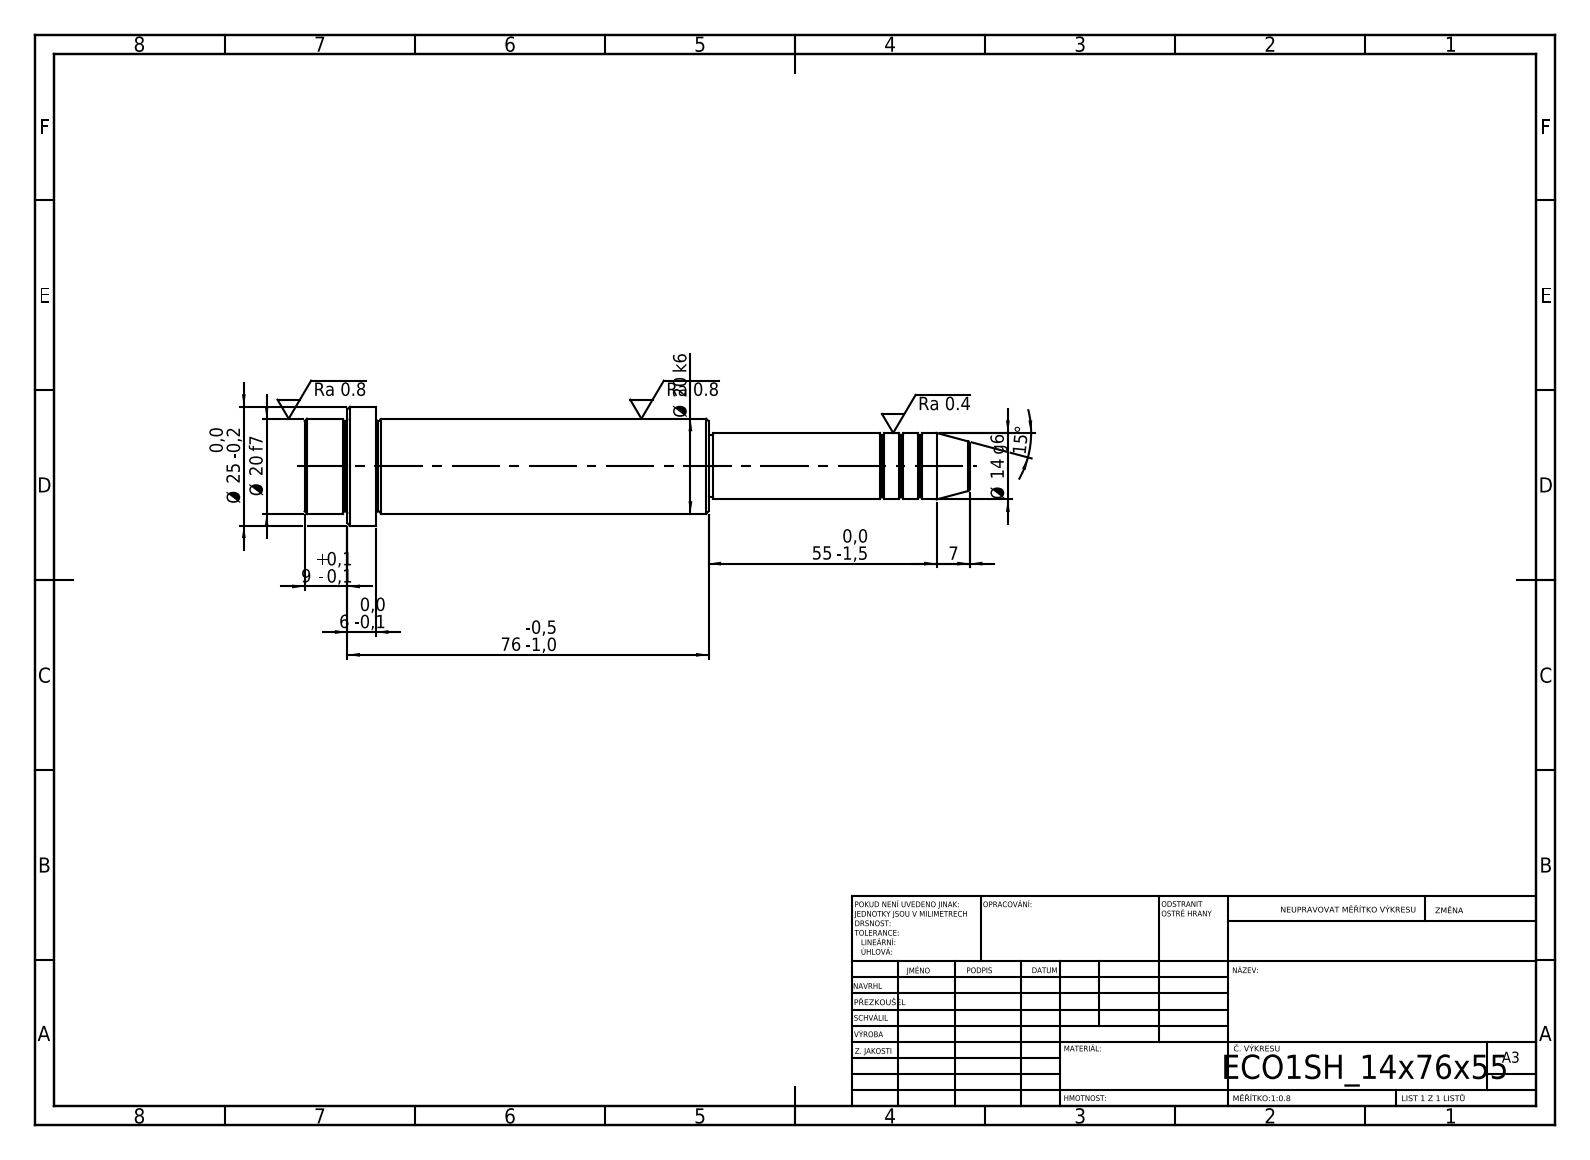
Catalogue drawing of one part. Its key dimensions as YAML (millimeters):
step_written_by: "SolidWorks 2019 (CONFIG_CONTROL_DESIGN)"
units: millimeters
bodies: {solids: 1, faces: 52, planar: 6, cylindrical: 16, other: 30}
overall_size: [140, 25, 25]
volume: 35822
surface_area: 8839
round_bosses_or_shafts:
  - {diameter: 25, count: 1}
  - {diameter: 20, count: 1}
  - {diameter: 14, count: 1}
  - {diameter: 13, count: 1}
face_to_face_distances: [15, 70, 85, 76, 6, 9, 55, 125, 131, 140]
